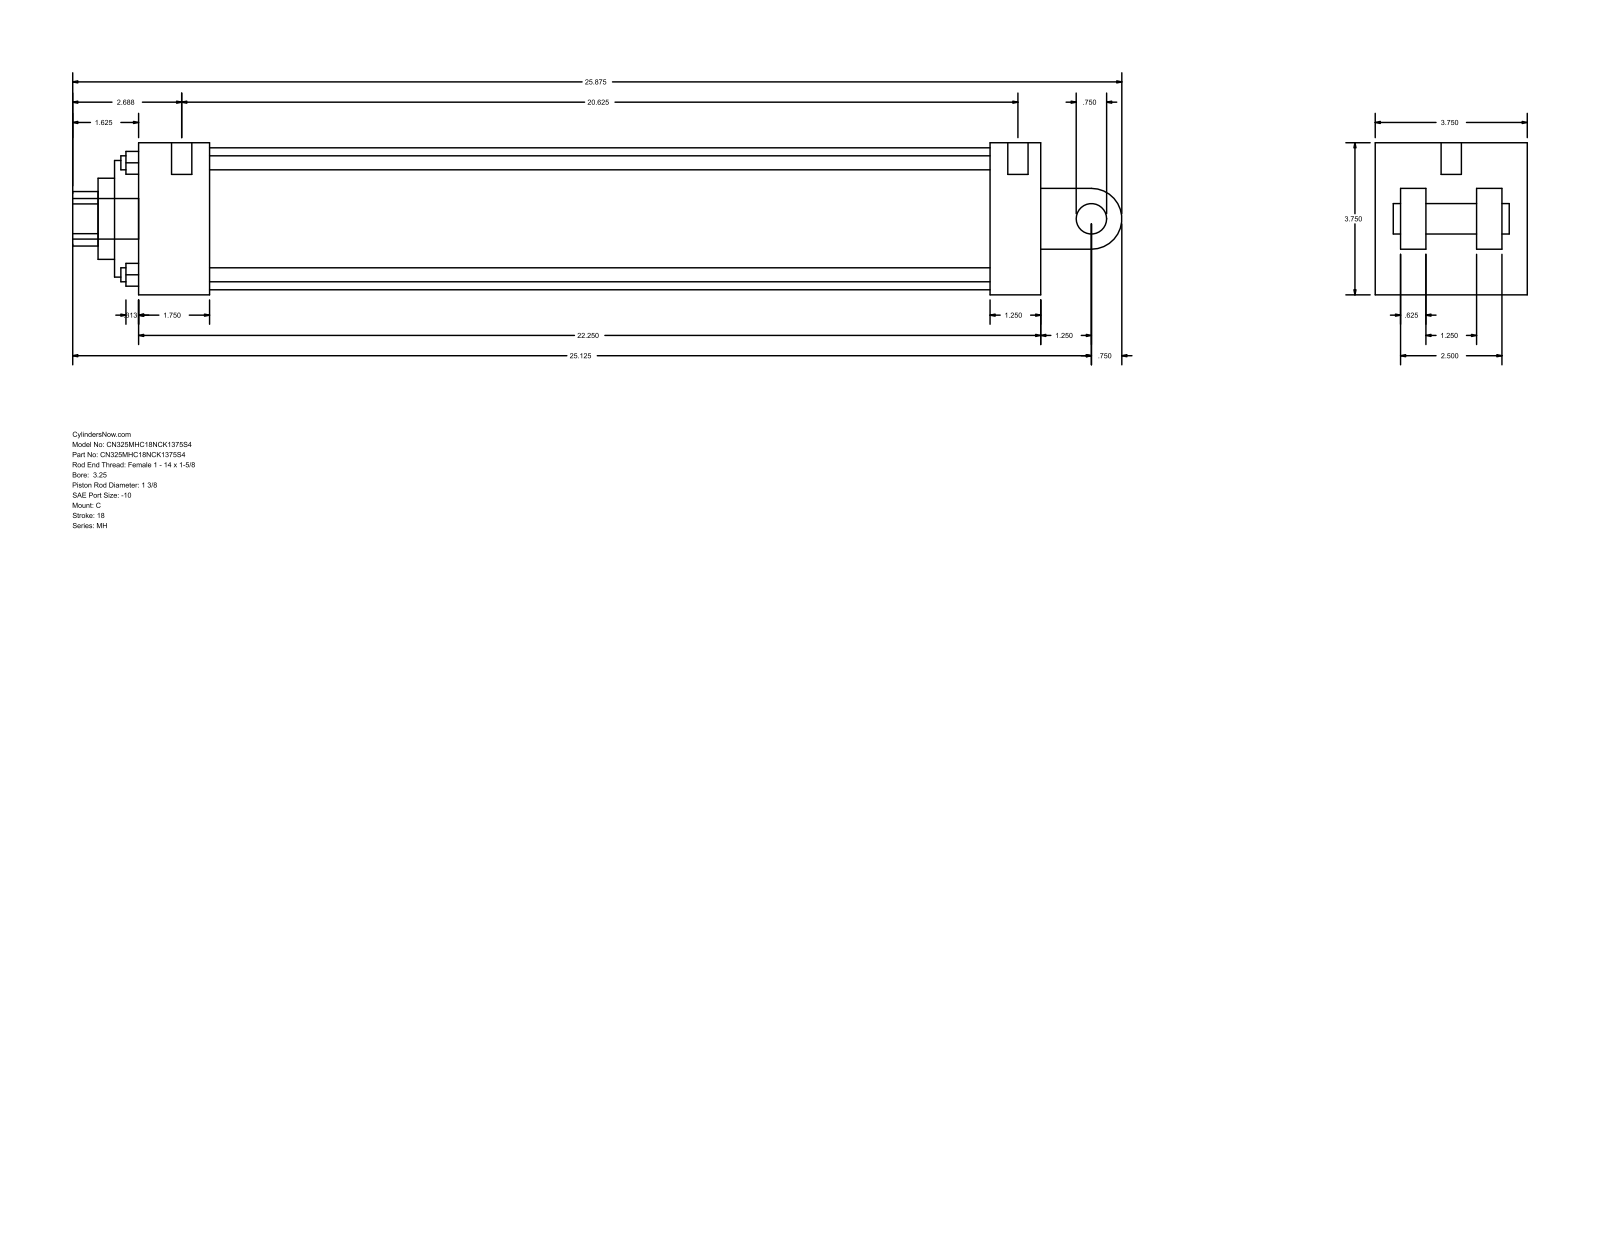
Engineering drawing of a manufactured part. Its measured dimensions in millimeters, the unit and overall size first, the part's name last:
Units: millimetres
Overall size (bounding box): 657.23 × 95.25 × 95.25
Round holes (diameter × count): ⌀8.76 ×4, ⌀5.56 ×2, ⌀12.7 ×1, ⌀34.92 ×1, ⌀50.8 ×1, ⌀73.03 ×1, ⌀88.9 ×1
Round bosses / shafts (diameter × count): ⌀5.56 ×2, ⌀25.4 ×1, ⌀19.05 ×1, ⌀12.7 ×1
Partial cylindrical surfaces — rounded edges, fillets, slot ends (radius × count): R17.06 ×1, R19.05 ×1
Main face-to-face distances: 95.24, 15.87, 565.15, 63.5, 31.74, 79.37, 47.63, 44.45, 533.4, 488.95
Hole centre spacings: 49.57, 70.1, 99.14, 4.76
Bodies: 0 solids, 101 faces (71 planar, 30 cylindrical, 0 other)
Part name (STEP PRODUCT): MH_C__0325_1.375
STEP written by: GSSL Pune (CONFIG_CONTROL_DESIGN)
